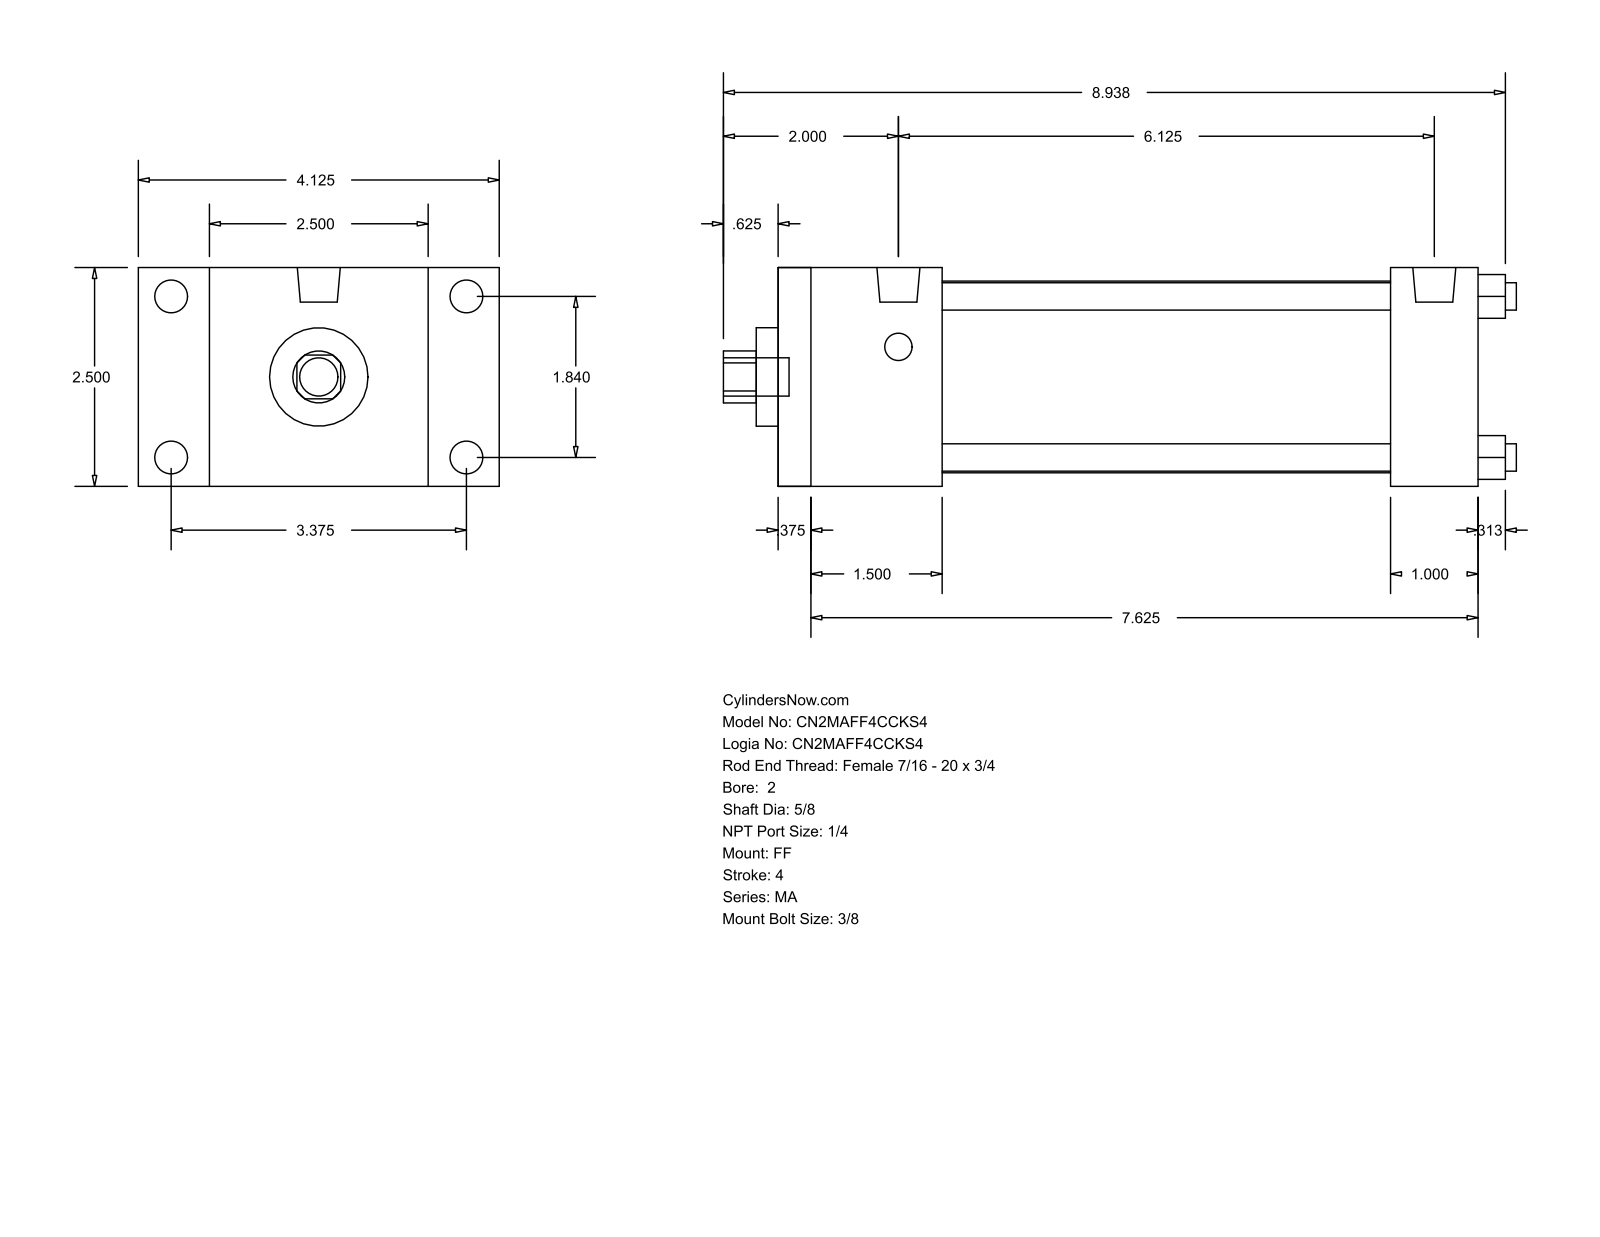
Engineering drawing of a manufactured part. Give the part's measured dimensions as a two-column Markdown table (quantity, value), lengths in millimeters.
| quantity | value |
| --- | --- |
| part name | MA_FF__0200_0.625 |
| STEP written by | GSSL Pune (CONFIG_CONTROL_DESIGN) |
| units | millimeters |
| bodies | 0 solids, 92 faces (64 planar, 28 cylindrical, 0 other) |
| overall size | 230.19 × 104.78 × 63.5 |
| round holes (diameter × count) | 7.94 × 4, 15.88 × 1, 28.57 × 1, 55.63 × 1 |
| round bosses / shafts (diameter × count) | 9.53 × 4, 7.94 × 4, 12.49 × 2, 11.11 × 1 |
| partial cylindrical surfaces (radius × count) | 7.54 × 1 |
| main face-to-face distances | 63.5, 203.19, 9.52, 193.67, 38.1, 47.62, 177.8, 168.28, 130.18, 155.57 |
| hole center spacings | 33.05, 46.74, 66.1 |
